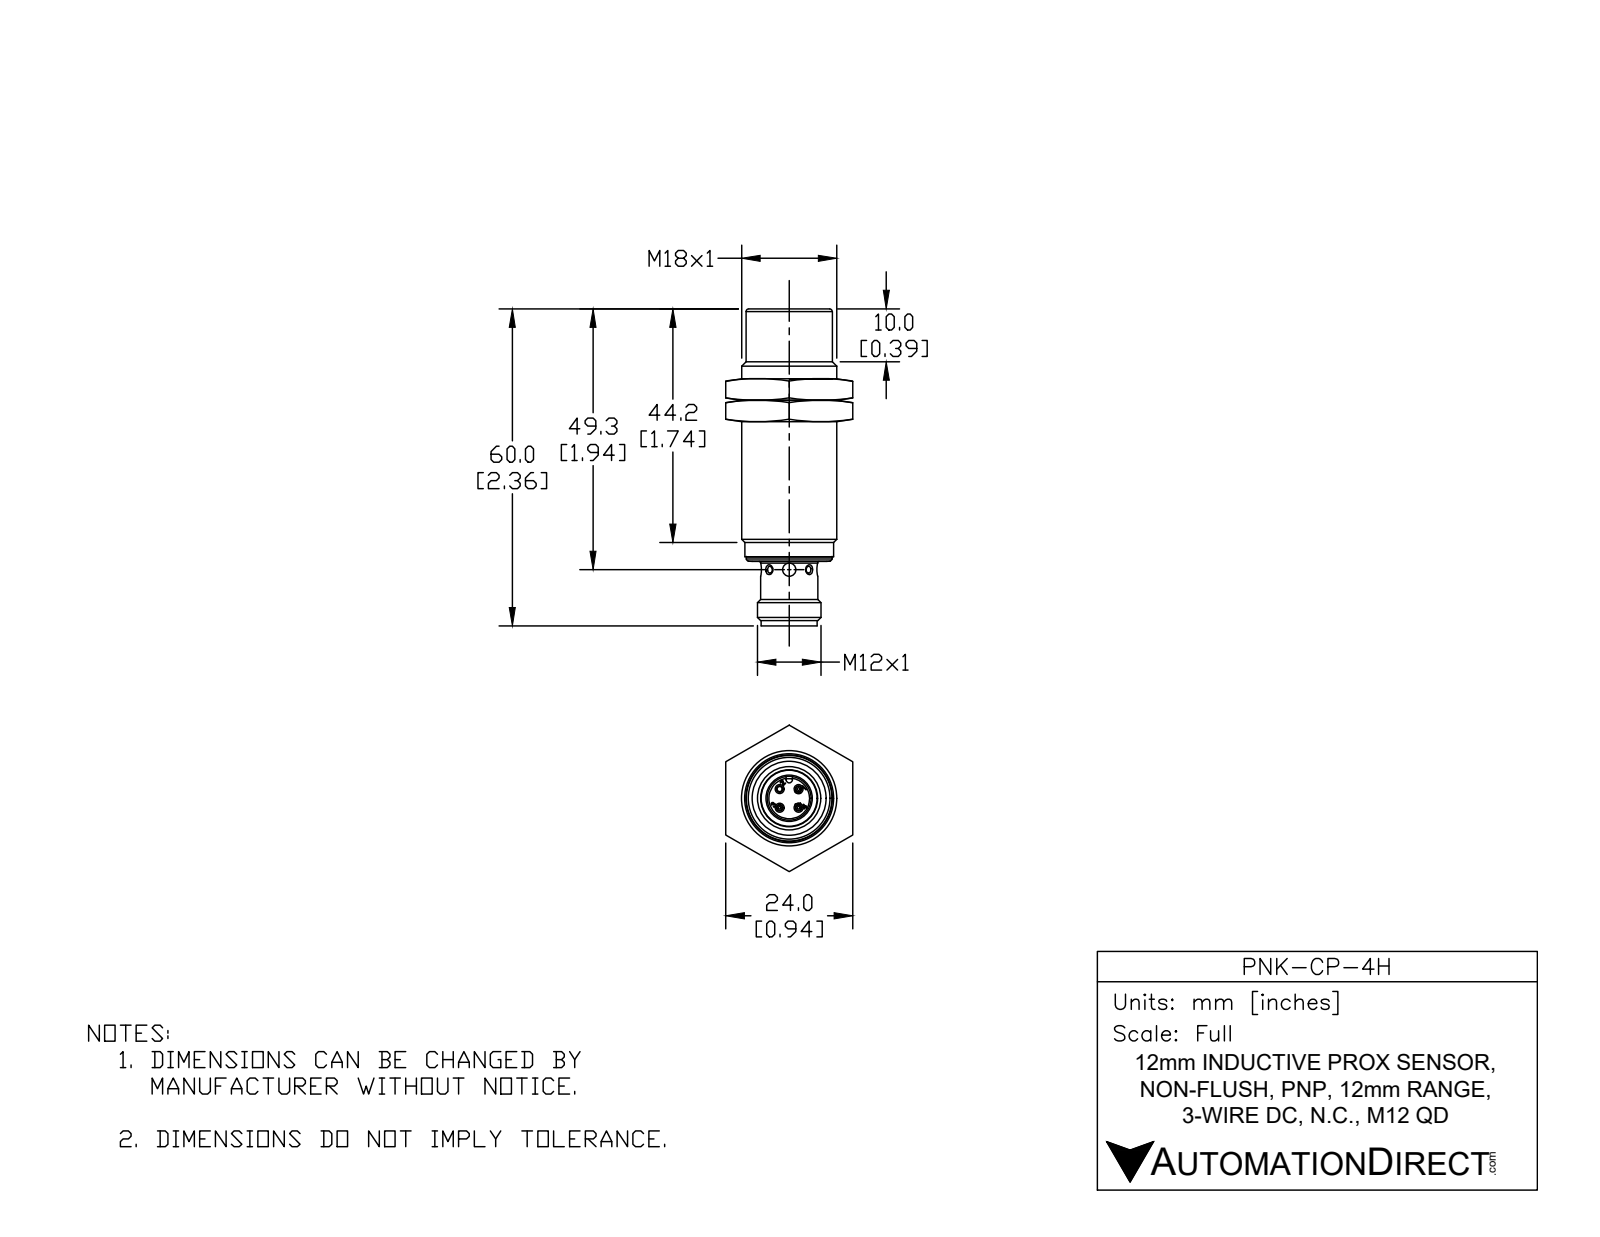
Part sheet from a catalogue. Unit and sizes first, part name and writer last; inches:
Units: inches
Overall size (bounding box): 2.362 × 0.709 × 0.709
Round holes (diameter × count): ⌀0.043 ×3, ⌀0.04 ×2, ⌀0.098 ×2, ⌀0.038 ×1, ⌀0.04 ×1, ⌀0.327 ×1, ⌀0.394 ×1, ⌀0.618 ×1, ⌀0.634 ×1
Round bosses / shafts (diameter × count): ⌀0.039 ×9, ⌀0.709 ×1, ⌀0.654 ×1, ⌀0.638 ×1, ⌀0.633 ×1, ⌀0.616 ×1, ⌀0.608 ×1, ⌀0.599 ×1
Partial cylindrical surfaces — rounded edges, fillets, slot ends (radius × count): R0.004 ×38, R0.024 ×1, R0.031 ×1, R0.161 ×1
Main face-to-face distances: 0.039, 0.022, 0.018, 1.87, 1.882, 1.86, 1.843, 1.848, 1.831, 2.323
Hole centre spacings: 0.098, 0.139, 0.197
Volume: 0.746 in³ · Surface area: 14.66 in²
Bodies: 1 solid, 1142 faces (751 planar, 150 cylindrical, 241 other)
Part name (STEP PRODUCT): PNK-CP-4H
STEP written by: SolidWorks 2017 (AUTOMOTIVE_DESIGN)
